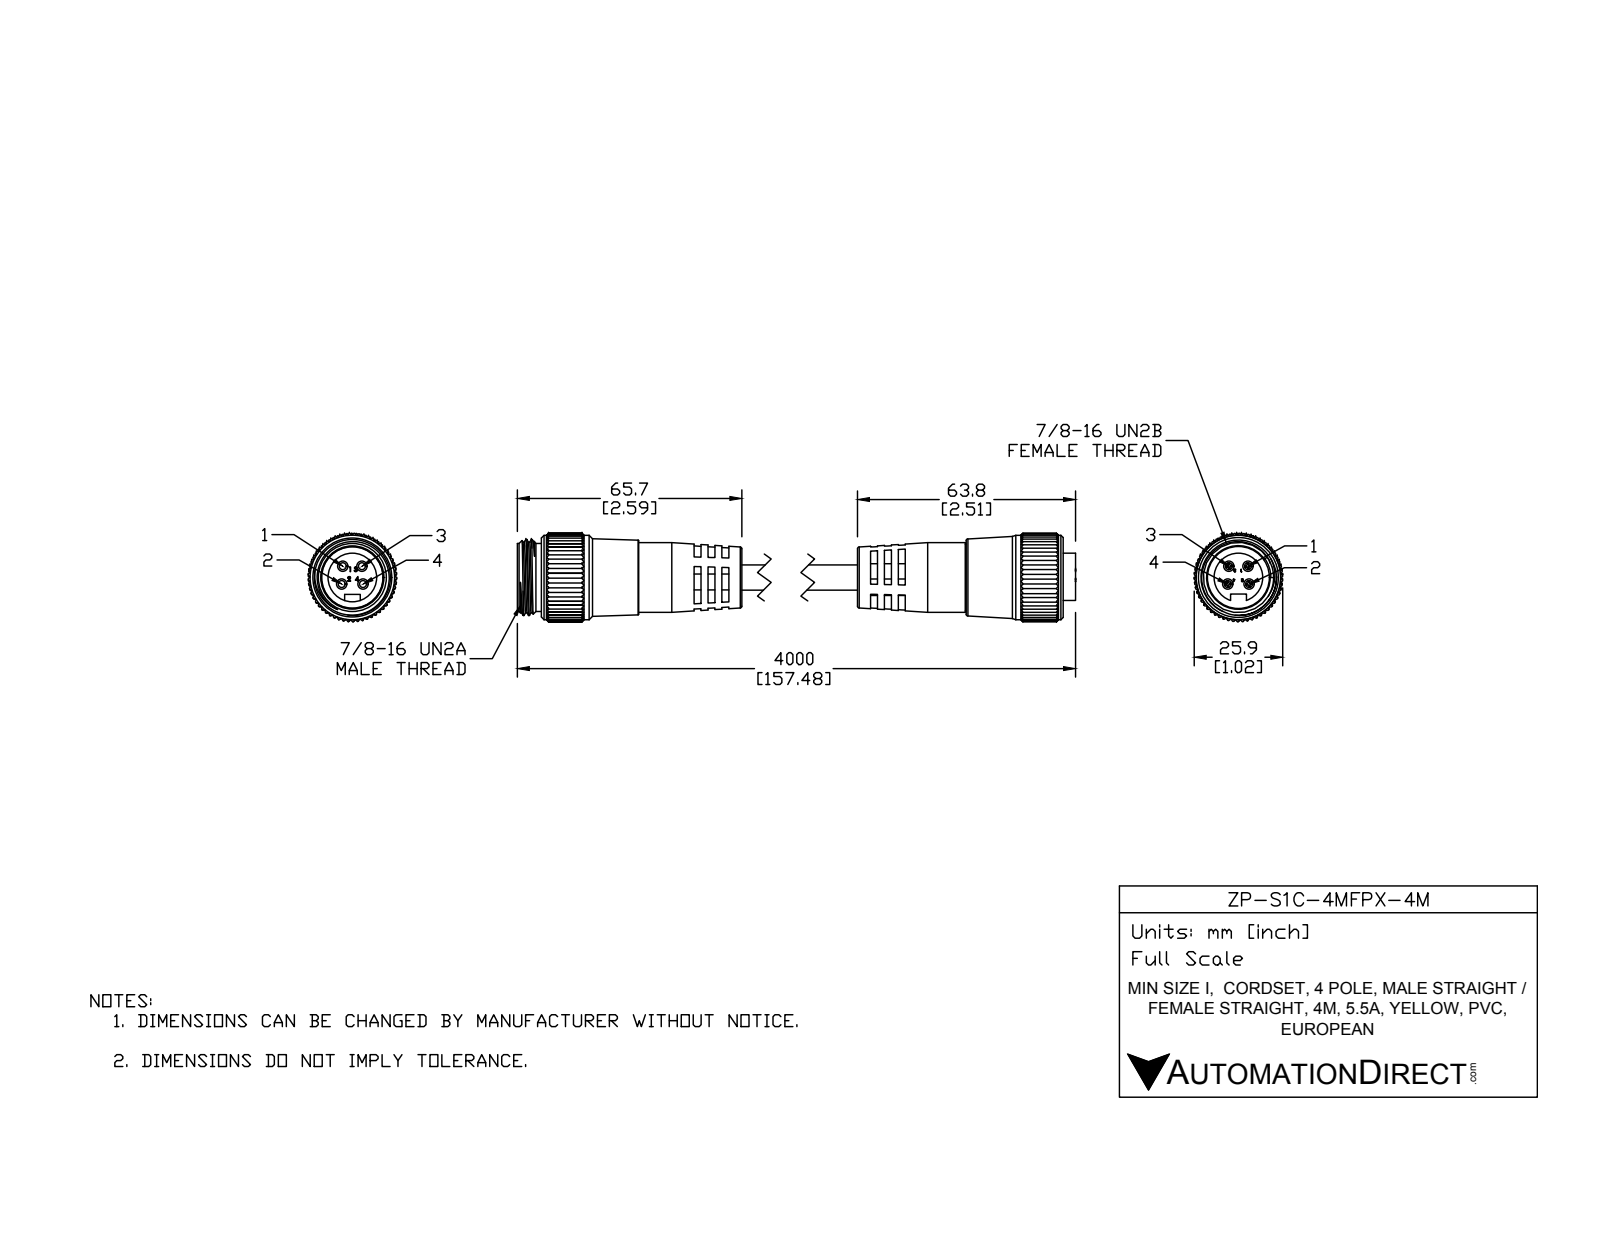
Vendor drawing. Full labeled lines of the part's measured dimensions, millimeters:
Part name (STEP PRODUCT): ZP-S1C-4MFPX-4M
STEP written by: SolidWorks 2015 (AUTOMOTIVE_DESIGN)
Units: millimetres
Bodies: 8 solids, 1161 faces (427 planar, 634 cylindrical, 100 other)
Overall size (bounding box): 229.66 × 25.84 × 25.83
Volume: 51 474 mm³ · Surface area: 24 731 mm²
Round holes (diameter × count): ⌀3.05 ×4, ⌀19.96 ×1, ⌀20.45 ×1, ⌀21 ×1
Round bosses / shafts (diameter × count): ⌀3.05 ×4, ⌀2 ×4, ⌀24.68 ×1, ⌀22.22 ×1, ⌀20.4 ×1, ⌀19.5 ×1, ⌀17.88 ×1, ⌀14.22 ×1
Partial cylindrical surfaces — rounded edges, fillets, slot ends (radius × count): R0.25 ×165, R2.29 ×1, R5.25 ×1, R12.93 ×1
Main face-to-face distances: 2, 4.02, 117.68, 113.65, 4.03, 125.74, 59.84, 4.04, 121.7, 121.72
Hole centre spacings: 3.67, 5.24, 4.32, 4.33, 5.59, 6.24, 7.89, 7.9
